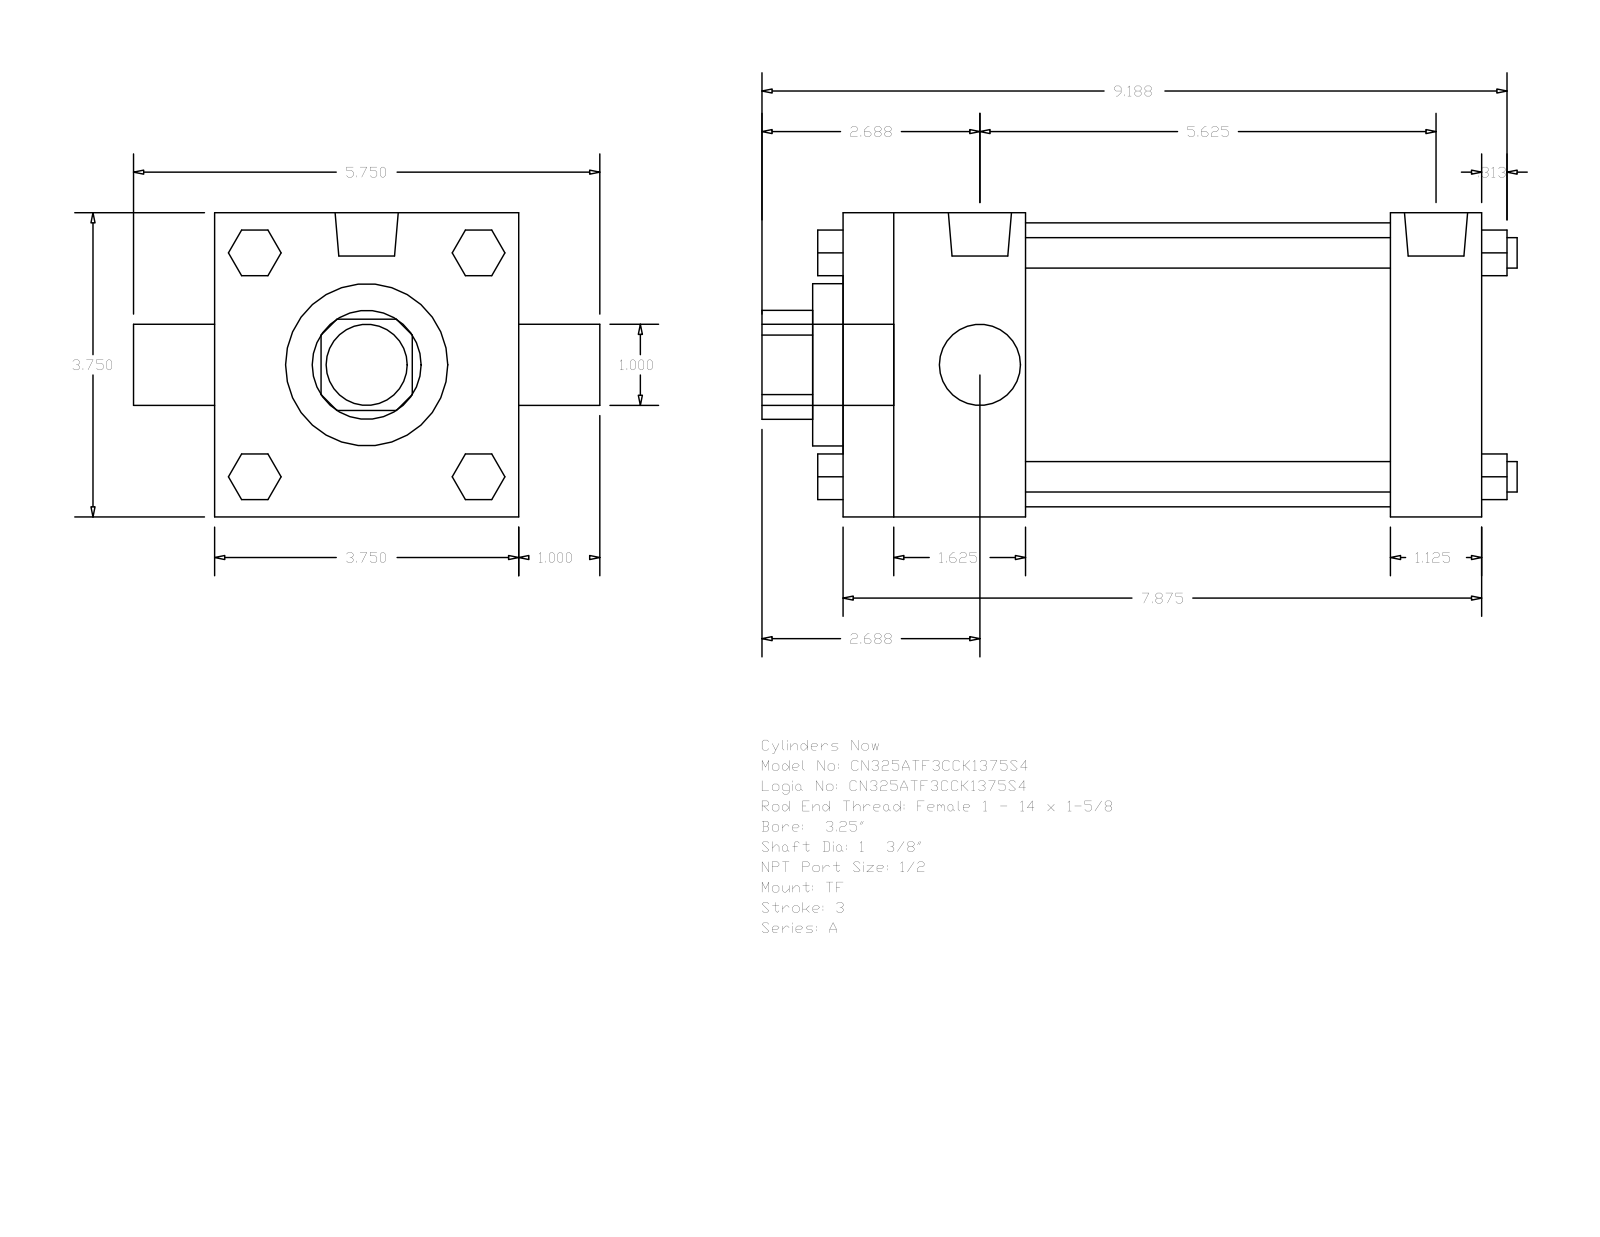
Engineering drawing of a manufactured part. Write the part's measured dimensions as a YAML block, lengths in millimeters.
part_name: "A_TF__0325_1.375"
step_written_by: "GSSL Pune (CONFIG_CONTROL_DESIGN)"
units: millimeters
bodies: {solids: 0, faces: 120, planar: 92, cylindrical: 28, other: 0}
overall_size: [236.54, 146.05, 95.25]
round_holes:
  - {diameter: 25.4, count: 1}
  - {diameter: 34.92, count: 1}
  - {diameter: 50.8, count: 1}
  - {diameter: 88.9, count: 1}
round_bosses_or_shafts:
  - {diameter: 9.53, count: 4}
  - {diameter: 8.73, count: 3}
  - {diameter: 19.77, count: 2}
  - {diameter: 25.4, count: 1}
partial_cylinders:
  - {radius: 17.06, count: 1}
face_to_face_distances: [95.24, 200.03, 28.58, 57.15, 171.45, 114.3, 142.88, 9.52, 66.67, 180.97]
